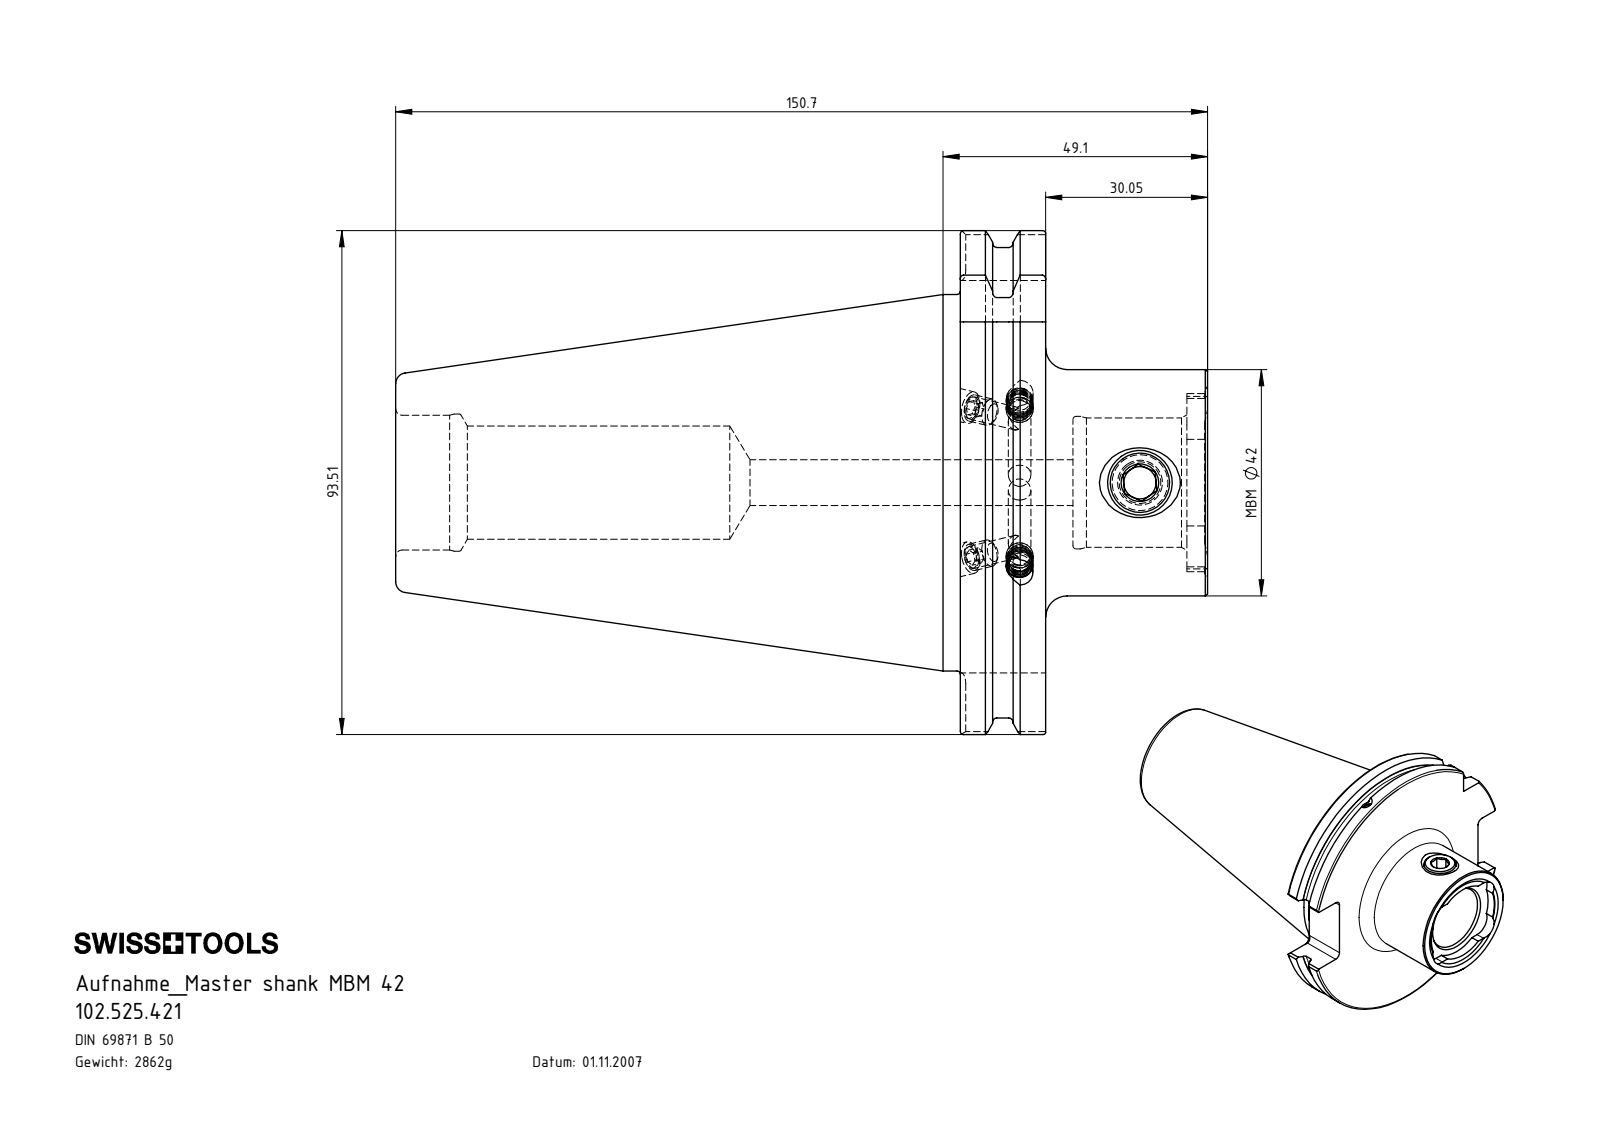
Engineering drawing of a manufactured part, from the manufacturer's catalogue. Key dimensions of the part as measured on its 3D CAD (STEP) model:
Part name (STEP PRODUCT): SB5-MB4.K01.049_C_mit Bundkhlung; MB4-ER1.001.013_A; ISO 4026 - M5 x 5_PreviewCfg; KVT_MB_600_050 (+1 more)
STEP written by: SolidWorks 2017 (CONFIG_CONTROL_DESIGN)
Units: millimetres
Bodies: 8 solids, 300 faces (79 planar, 82 cylindrical, 139 other)
Overall size (bounding box): 150.7 × 97.45 × 93.51
Volume: 364 576 mm³ · Surface area: 49 754 mm²
Round holes (diameter × count): ⌀4.2 ×3, ⌀6 ×3, ⌀4 ×2, ⌀5 ×1, ⌀8.5 ×1, ⌀11 ×1, ⌀21 ×1, ⌀24 ×1, ⌀24.6 ×1, ⌀25 ×1, ⌀25.45 ×1
Round bosses / shafts (diameter × count): ⌀5 ×3, ⌀91 ×1, ⌀69.85 ×1, ⌀42 ×1, ⌀12 ×1
Partial cylindrical surfaces — rounded edges, fillets, slot ends (radius × count): R2 ×8, R5.2 ×4, R14.9 ×1, R16.52 ×1, R48.73 ×1
Main face-to-face distances: 15.85, 104.8, 120.65, 21.15, 125.7, 20.9, 5.05, 72.8, 146.85, 42.05
